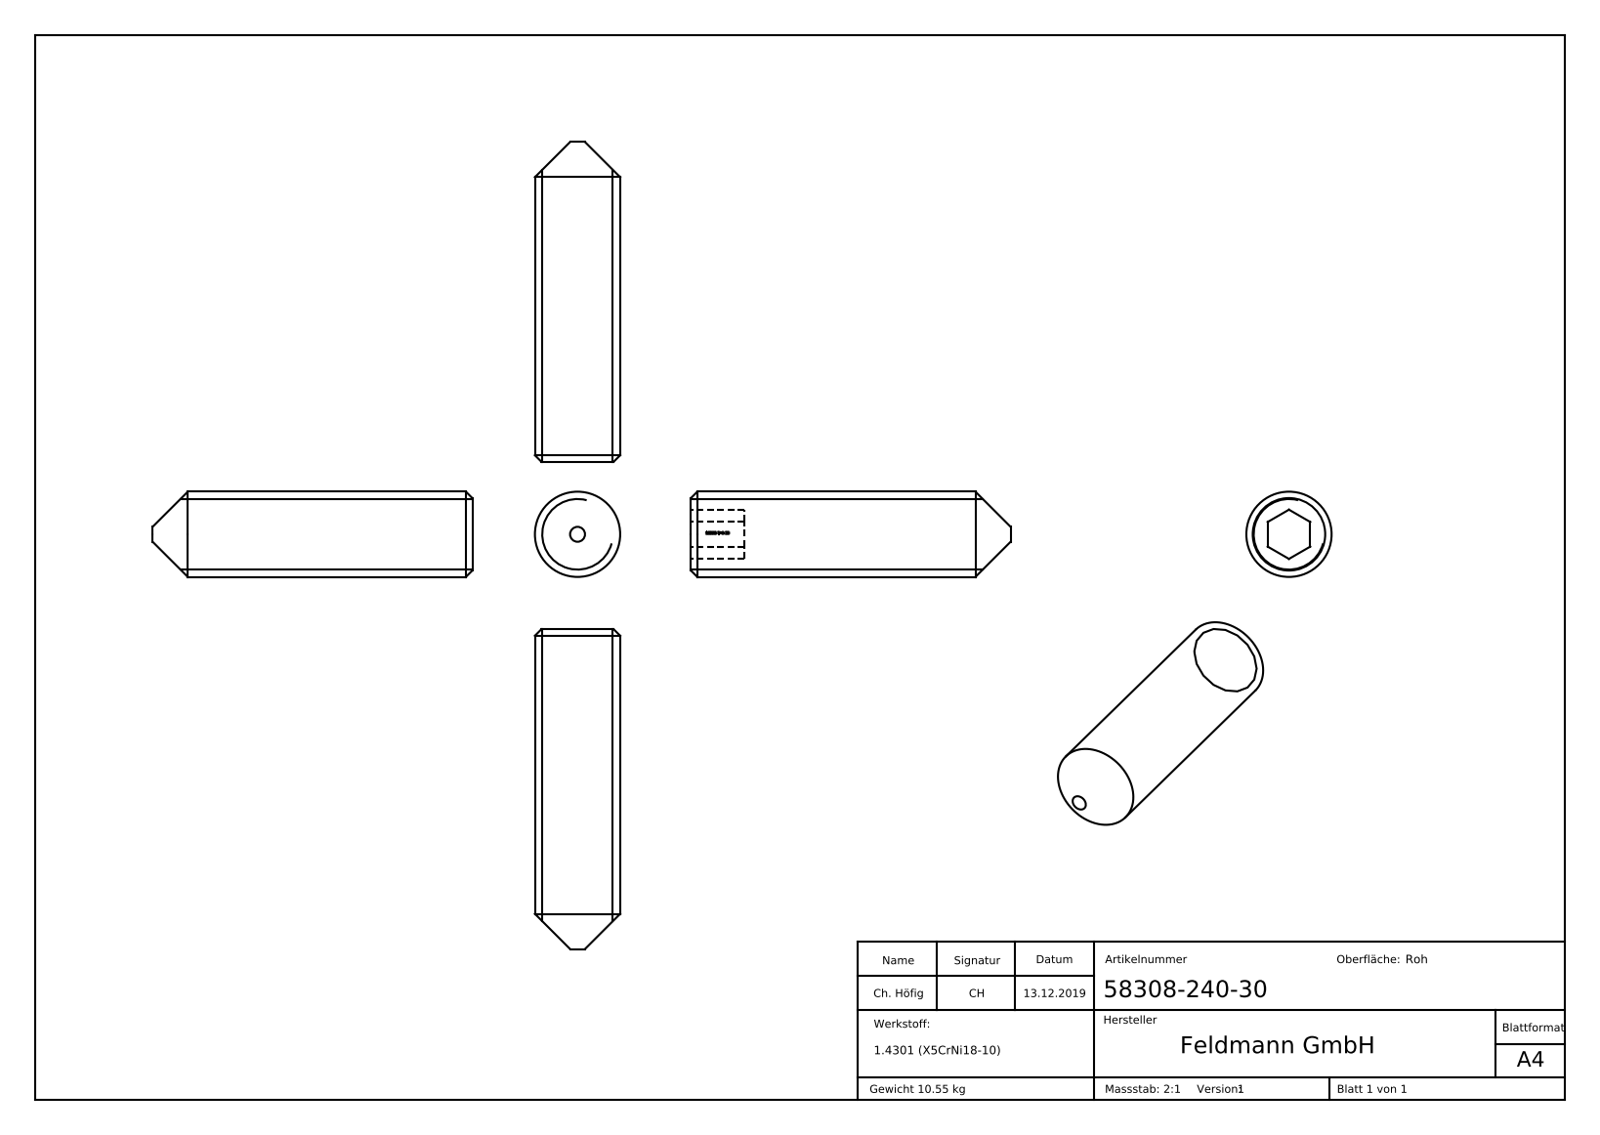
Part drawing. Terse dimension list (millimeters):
name: 58308-240-30
written by: SolidWorks 2015 (CONFIG_CONTROL_DESIGN)
unit: mm
bodies: 1 solid, 179 faces (68 planar, 1 cylindrical, 110 other)
size: 70 × 8 × 8
volume: 1 335 mm³; area: 853 mm²
bosses: 1× ⌀8
face distances: 4, 5, 25, 30, 4.1, 27.15, 2.15, 2.85, 27.19, 2.19
